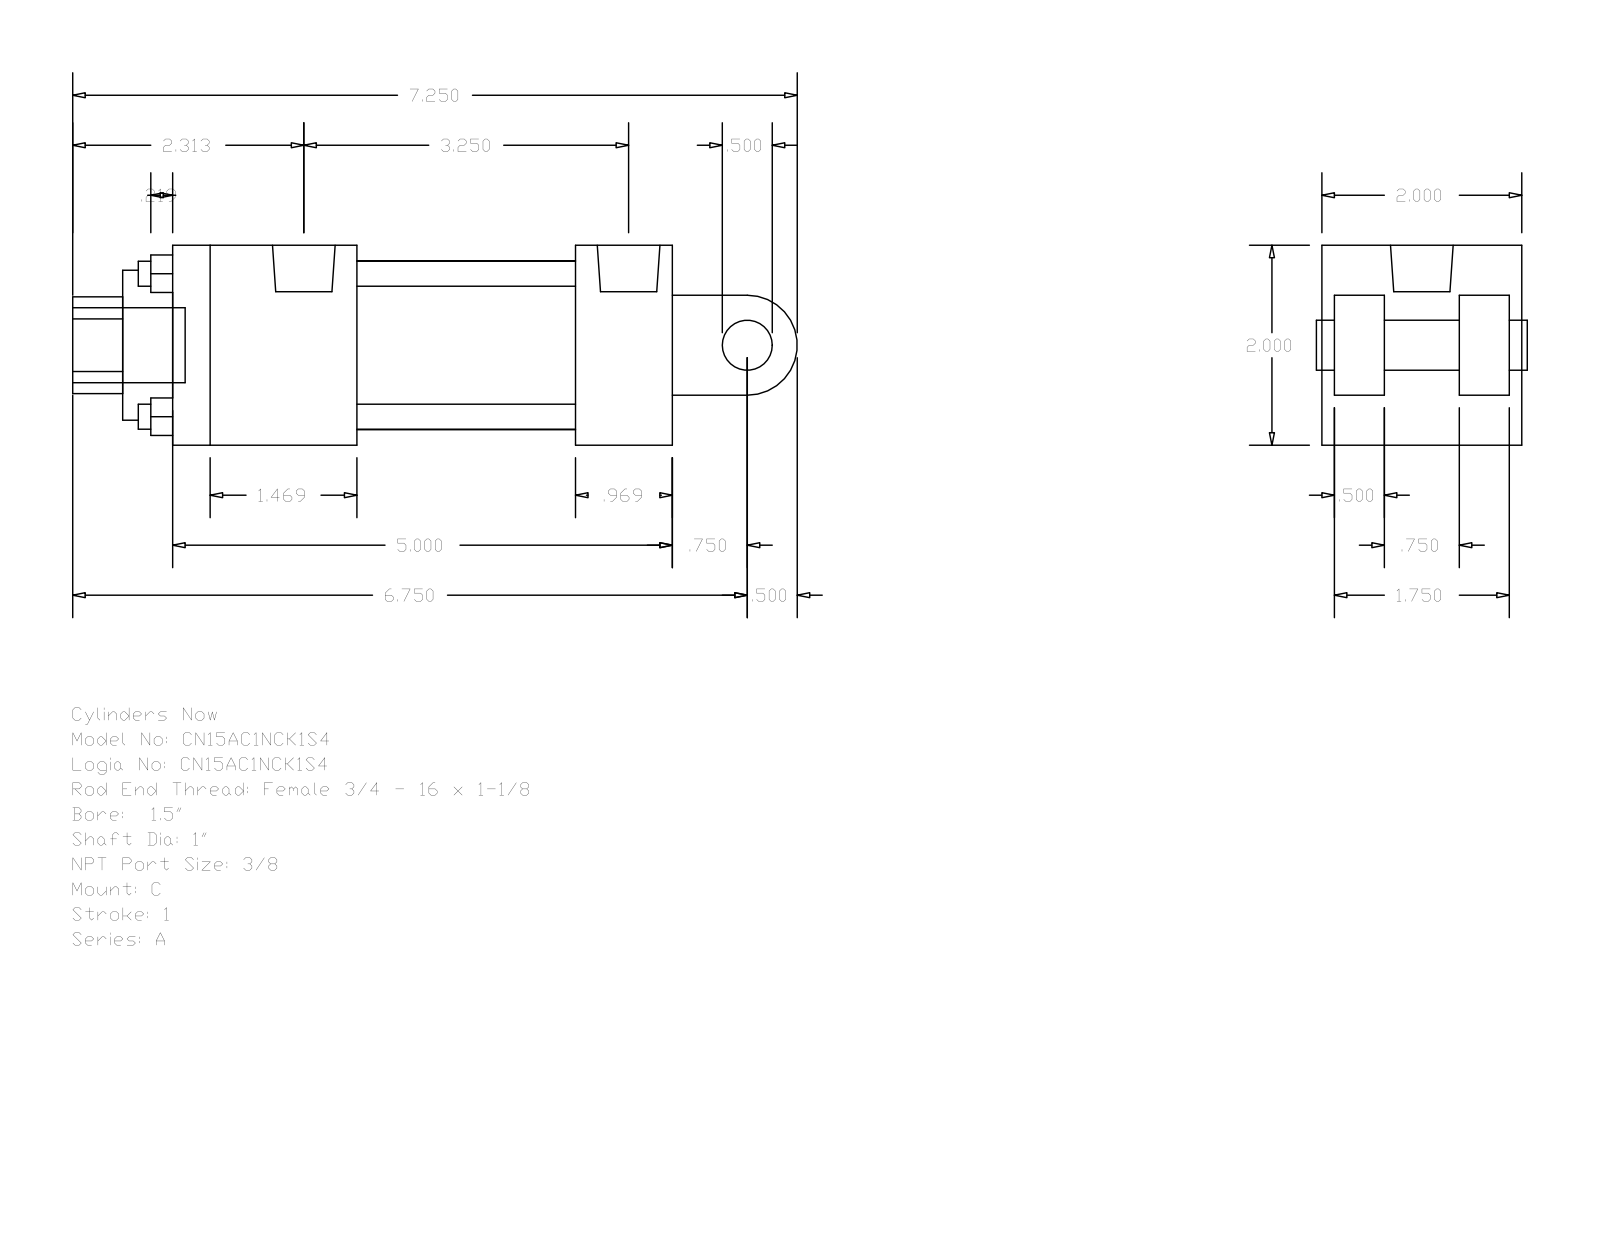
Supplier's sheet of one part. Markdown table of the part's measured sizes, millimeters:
| quantity | value |
| --- | --- |
| part name | A_C__0150_1 |
| STEP written by | GSSL Pune (CONFIG_CONTROL_DESIGN) |
| units | millimeters |
| bodies | 0 solids, 99 faces (70 planar, 29 cylindrical, 0 other) |
| overall size | 184.15 × 50.8 × 50.8 |
| round holes (diameter × count) | 6.35 × 4, 5.56 × 2, 15.93 × 1, 25.4 × 1, 38.1 × 1, 42.93 × 1 |
| round bosses / shafts (diameter × count) | 5.56 × 2, 19.05 × 1, 15.93 × 1, 12.7 × 1 |
| partial cylindrical surfaces (radius × count) | 12.29 × 1, 12.7 × 1 |
| main face-to-face distances | 50.8, 12.7, 3.17, 15.87, 47.63, 34.93, 31.76, 55.56, 127, 102.39 |
| hole center spacings | 25.68, 36.32, 51.36, 3.97 |
